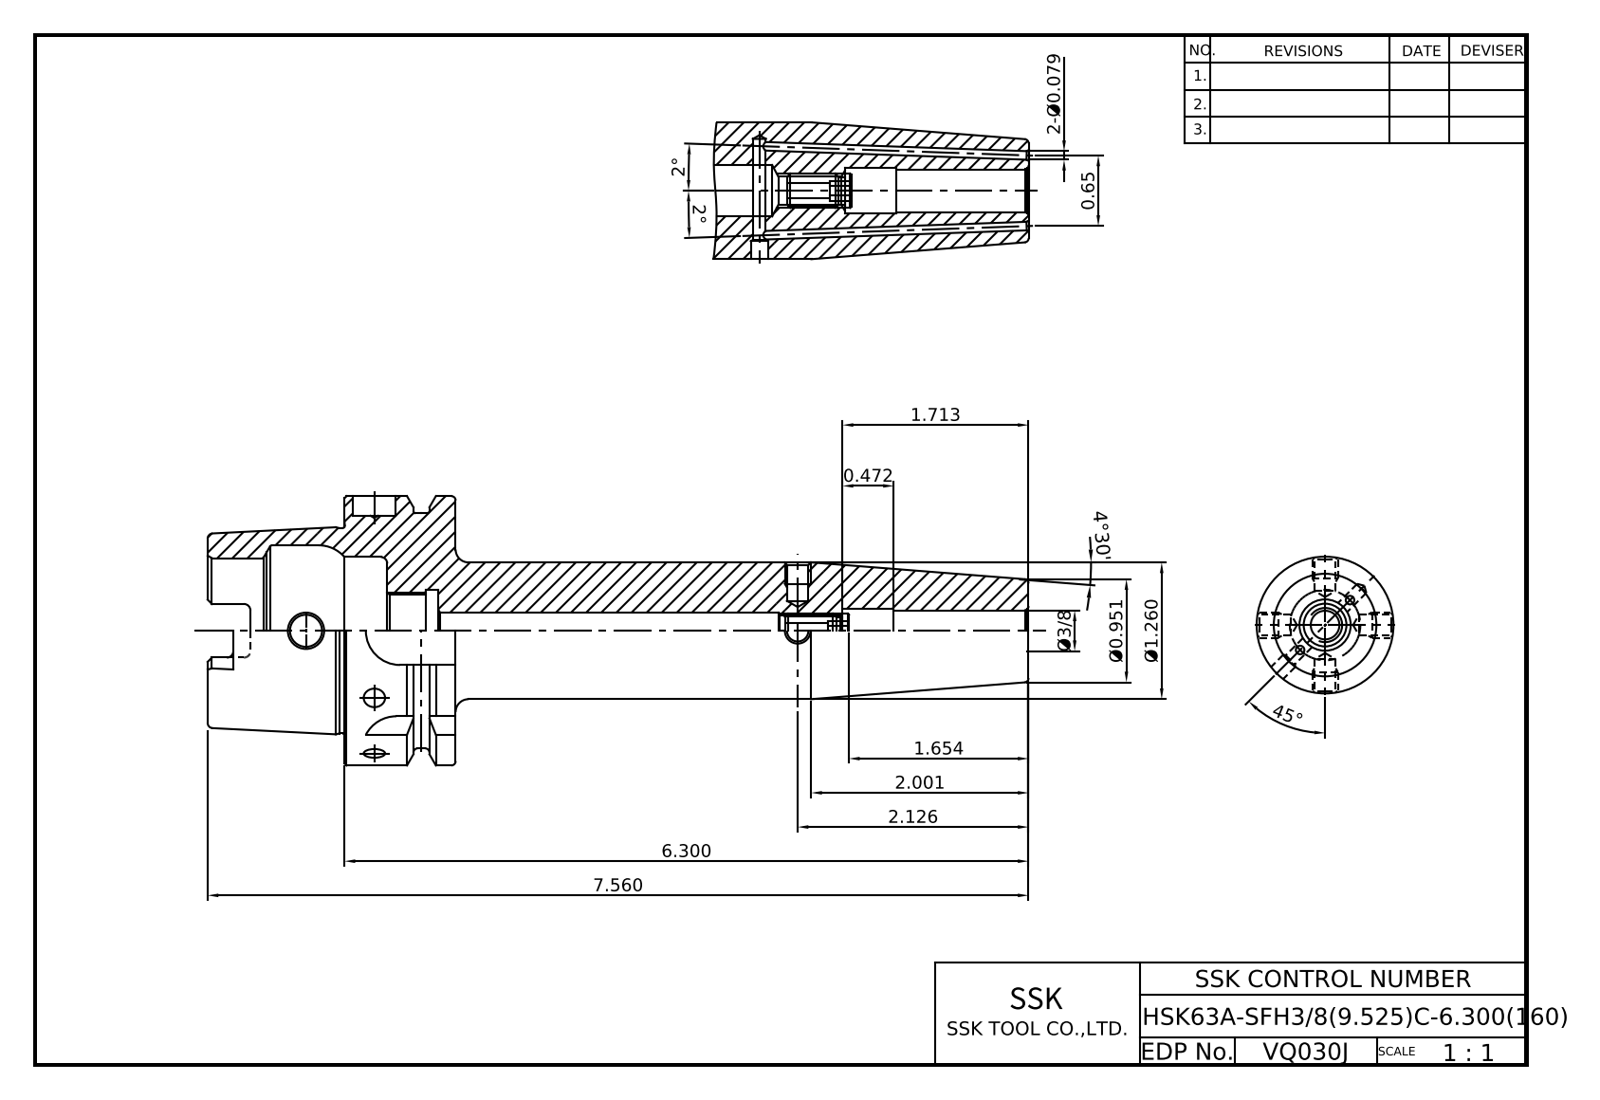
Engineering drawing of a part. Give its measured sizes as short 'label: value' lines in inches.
name: VQ030J-HSK63A-SFH0_375C-6_30
written by: CREO PARAMETRIC BY PTC INC, 2018100 (CONFIG_CONTROL_DESIGN)
unit: in
bodies: 1 solid, 208 faces (65 planar, 73 cylindrical, 70 other)
size: 7.559 × 2.48 × 2.48
volume: 10.43 in³; area: 63.44 in²
holes: 2× ⌀0.079, 2× ⌀0.197, 2× ⌀0.236, 1× ⌀0.276, 1× ⌀0.295, 1× ⌀0.315, 1× ⌀0.331, 1× ⌀0.375, 1× ⌀0.394, 1× ⌀0.398, 1× ⌀0.669, 1× ⌀0.709
bosses: 1× ⌀2.48, 1× ⌀2.165, 1× ⌀1.891, 1× ⌀1.26
rounds: 6× R0.059, 4× R0.113, 4× R0.315
face distances: 1.024, 0.394, 0.63, 1.26, 0.241, 0.389, 1.654, 2.283, 0.157, 0.866
hole spacings: 3.898, 4.528
